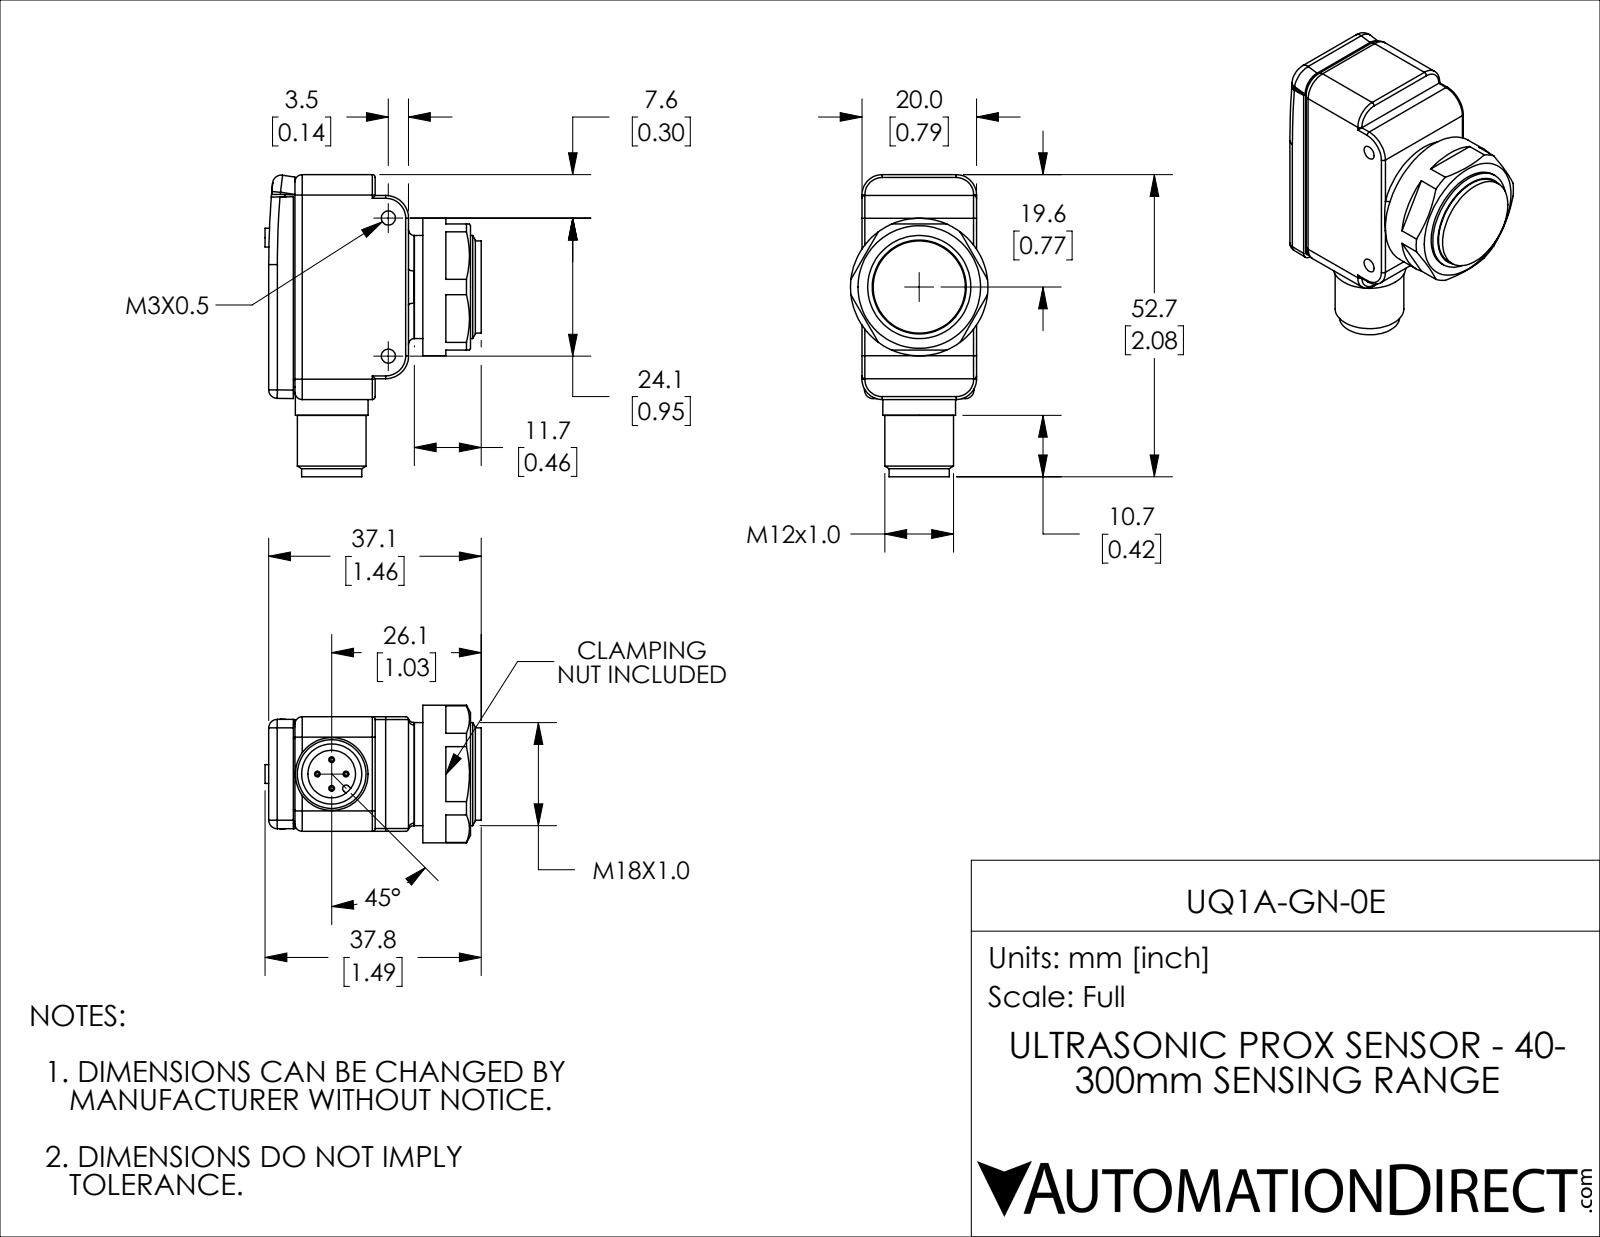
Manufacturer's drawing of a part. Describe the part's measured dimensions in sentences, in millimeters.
The part is named "UQ1A-GN-0E". Its 3-D file was written by "SolidWorks 2018 (AUTOMOTIVE_DESIGN)". It is 7 solids with 203 faces: 81 planar, 72 cylindrical and 50 other. Overall it measures 52.73 by 37.75 by 24 millimeters. Its volume is 22 757 cubic millimeters and its surface area 11 051 square millimeters. Round holes: 2 of diameter 2.46, 1 of diameter 3.3, 1 of diameter 8.3. Round bosses or shafts: 4 of diameter 1, 1 of diameter 24, 1 of diameter 18, 1 of diameter 16.1, 1 of diameter 12.7, 1 of diameter 12, 1 of diameter 10.5. Partial cylindrical surfaces (rounded edges, fillets, slot ends): 10 of radius 0.5, 6 of radius 1.5, 4 of radius 1.25, 4 of radius 3.55, 2 of radius 3, 2 of radius 4, 2 of radius 150, 1 of radius 0.6. The main face-to-face distances are 2.3, 20, 23.13, 20.83, 2.29, 4.59, 25.42, 11.67, 37.09, 34.8. The hole center spacings are 24.1.
